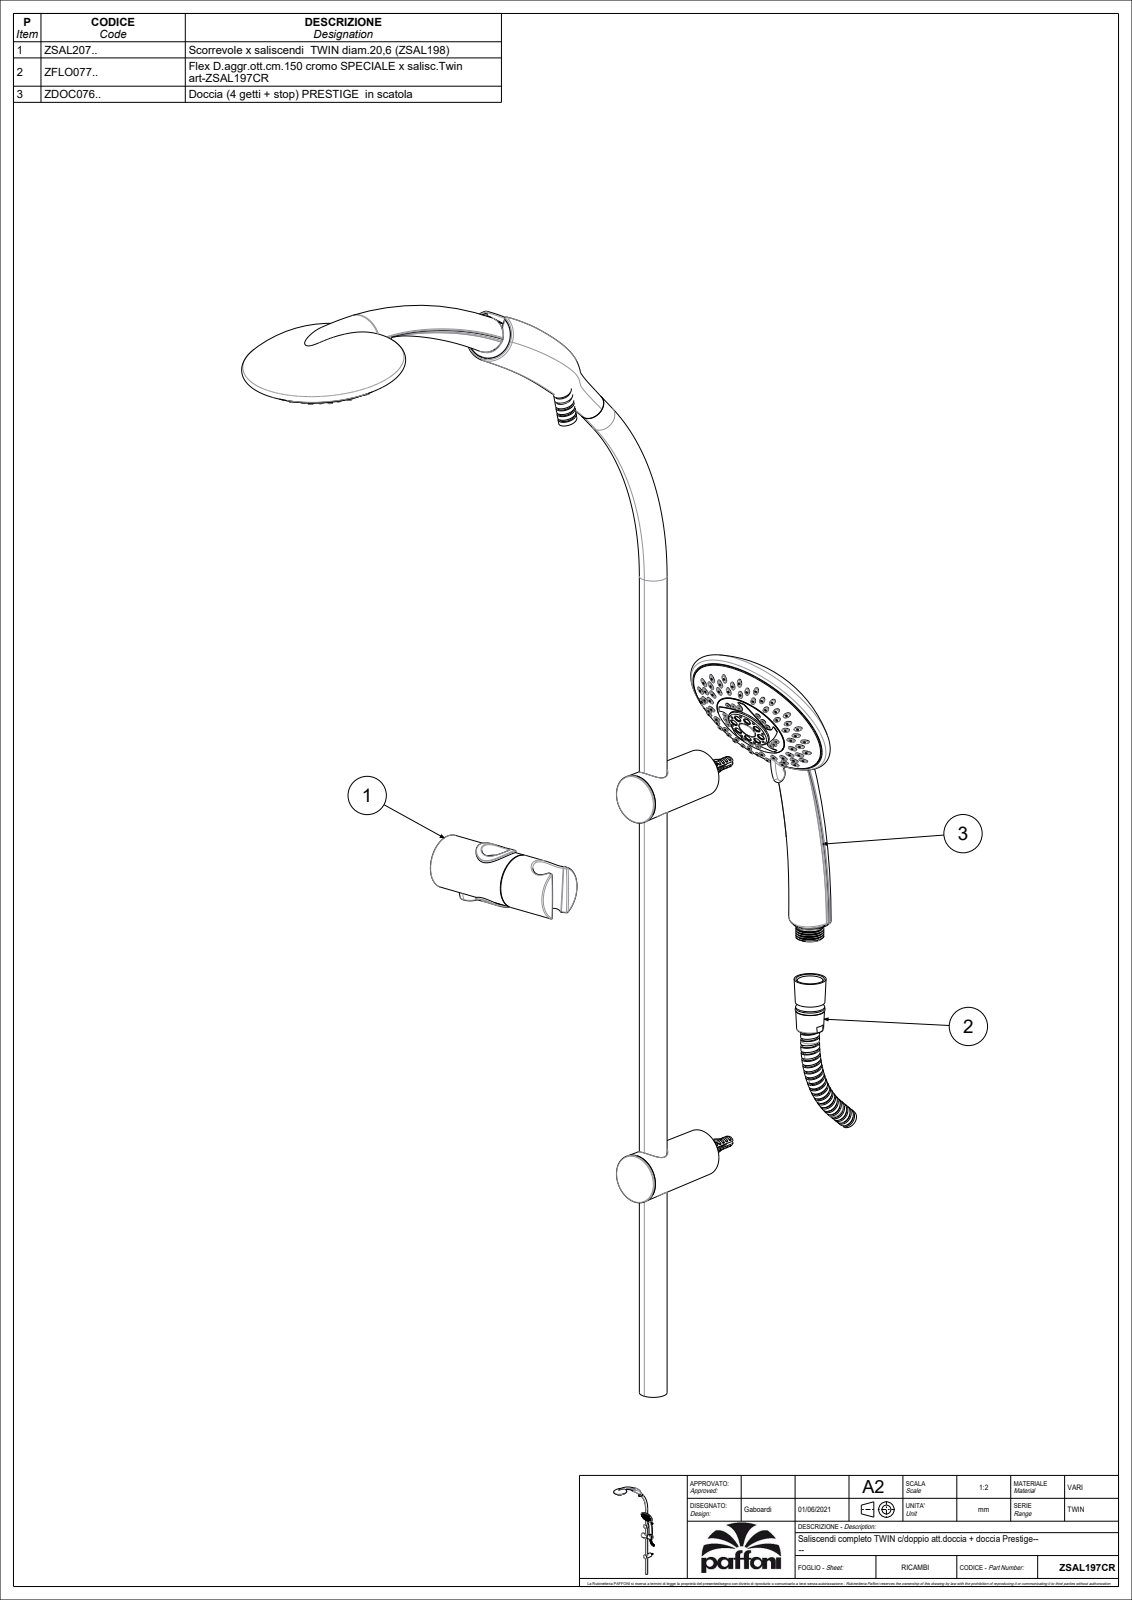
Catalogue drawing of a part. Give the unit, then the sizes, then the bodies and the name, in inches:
Units: inches
Overall size (bounding box): 37.251 × 19.545 × 4.848
Round holes (diameter × count): ⌀0.059 ×63, ⌀0.043 ×32, ⌀0.079 ×21, ⌀0.098 ×15, ⌀0.096 ×8, ⌀0.232 ×8, ⌀0.118 ×7, ⌀0.15 ×3, ⌀0.276 ×3, ⌀0.551 ×3, ⌀0.13 ×2, ⌀0.157 ×2
Round bosses / shafts (diameter × count): ⌀0.165 ×15, ⌀0.244 ×3, ⌀2.323 ×2, ⌀1.437 ×2, ⌀1.378 ×2, ⌀1.228 ×2, ⌀0.78 ×2, ⌀0.472 ×2
Partial cylindrical surfaces — rounded edges, fillets, slot ends (radius × count): R0.02 ×66, R0.039 ×33, R0.079 ×12, R0.012 ×9, R0.059 ×9, R0.087 ×8, R3.43 ×7, R0.024 ×6
Main face-to-face distances: 0.098, 0.02, 0.079, 0.189, 0.209, 0.118, 0.091, 7.594, 0.106, 0.059
Hole centre spacings: 0.63, 0.467, 0.768, 0.466, 0.63, 0.842, 0.579, 0.63
Volume: 27.4 in³ · Surface area: 694.2 in²
Bodies: 51 solids, 4533 faces (1170 planar, 1251 cylindrical, 2112 other)
Part name (STEP PRODUCT): M50540-016_3; M50380-030_1; M50380-032_2; M50520-011_2 (+8 more)
STEP written by: CREO PARAMETRIC BY PTC INC, 2020044 (CONFIG_CONTROL_DESIGN)
